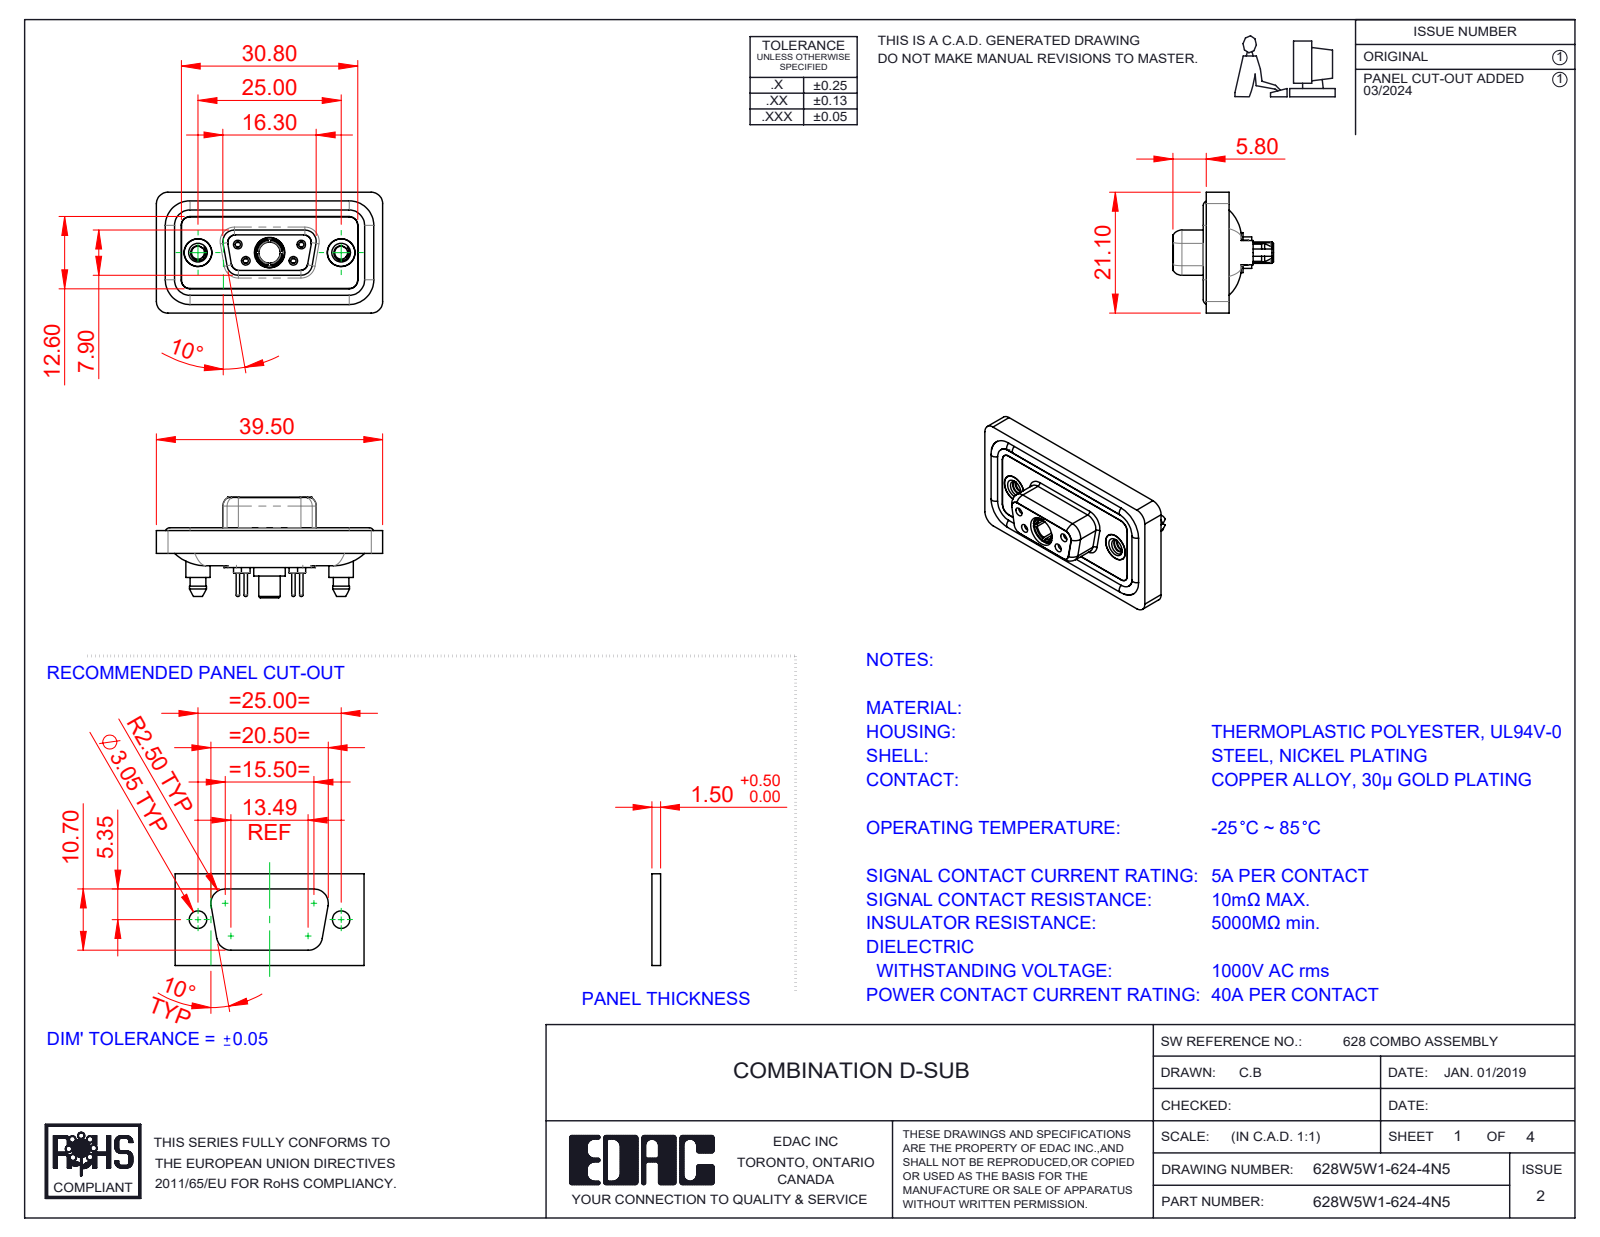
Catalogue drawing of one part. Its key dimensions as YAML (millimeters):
part_name: "628Combo Contact Row 2_24; 628Combo Housing_5W1; 628Combo Contact Row 1_24; 628Combo Shell Rear_09 Contacts (+5 more)"
step_written_by: "SolidWorks 2023 (CONFIG_CONTROL_DESIGN)"
units: millimeters
bodies: {solids: 13, faces: 730, planar: 210, cylindrical: 319, other: 201}
overall_size: [39.5, 21.1, 17.55]
volume: 4919
surface_area: 7979
round_holes:
  - {diameter: 0.9, count: 4}
  - {diameter: 1.1, count: 4}
  - {diameter: 1.5, count: 4}
  - {diameter: 2, count: 4}
  - {diameter: 4.85, count: 3}
  - {diameter: 1.6, count: 2}
  - {diameter: 1.7, count: 2}
  - {diameter: 2.26, count: 2}
  - {diameter: 4, count: 2}
  - {diameter: 4.05, count: 2}
  - {diameter: 5, count: 2}
  - {diameter: 3.7, count: 1}
round_bosses_or_shafts:
  - {diameter: 1.6, count: 6}
  - {diameter: 2.2, count: 4}
  - {diameter: 0.6, count: 4}
  - {diameter: 5.4, count: 2}
  - {diameter: 4.95, count: 2}
  - {diameter: 4.8, count: 2}
  - {diameter: 4.25, count: 2}
  - {diameter: 5.5, count: 1}
partial_cylinders:
  - {radius: 1.5, count: 24}
  - {radius: 2, count: 18}
  - {radius: 1.6, count: 10}
  - {radius: 1.35, count: 8}
  - {radius: 0.25, count: 4}
  - {radius: 0.5, count: 4}
  - {radius: 0.6, count: 4}
  - {radius: 0.65, count: 4}
face_to_face_distances: [0.4, 2.9, 1.1, 1.8, 1.6, 0.5, 5.65, 7.45, 5.35, 3.6]
hole_center_spacings: [3.16, 5.72, 7.1, 12.5, 18.1, 4.39, 4.4, 8.31]
